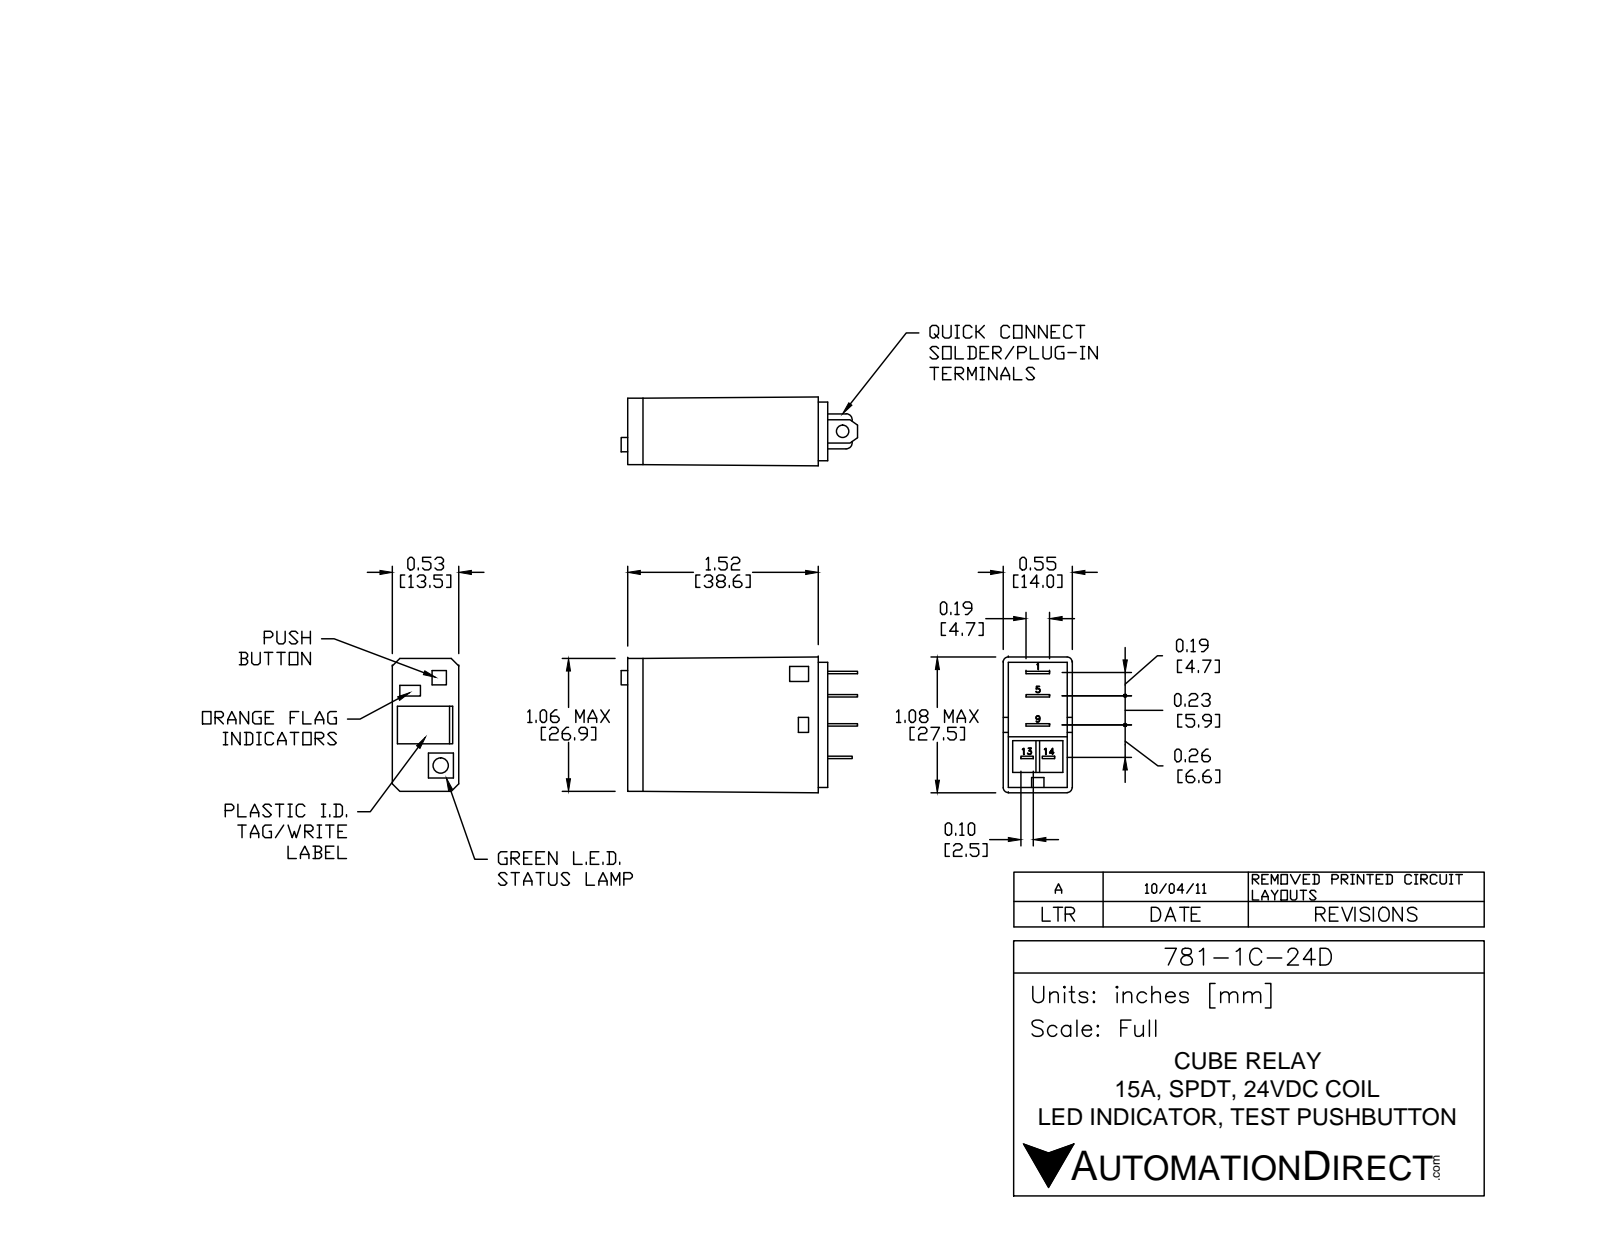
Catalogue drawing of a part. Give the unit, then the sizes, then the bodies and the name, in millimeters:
Units: millimetres
Overall size (bounding box): 47.35 × 27.5 × 14.12
Round holes (diameter × count): ⌀1.85 ×1
Round bosses / shafts (diameter × count): ⌀0.83 ×1
Partial cylindrical surfaces — rounded edges, fillets, slot ends (radius × count): R0.5 ×4, R0.56 ×4, R1.5 ×4, R1.32 ×2, R3.78 ×1
Main face-to-face distances: 14, 35.5, 27.5, 1.75, 37.25, 40.25, 38.5, 3, 2, 39.25
Volume: 15 230 mm³ · Surface area: 5 981 mm²
Bodies: 10 solids, 261 faces (176 planar, 30 cylindrical, 55 other)
Part name (STEP PRODUCT): 781-1C-24D
STEP written by: SolidWorks 2013 (AUTOMOTIVE_DESIGN)
